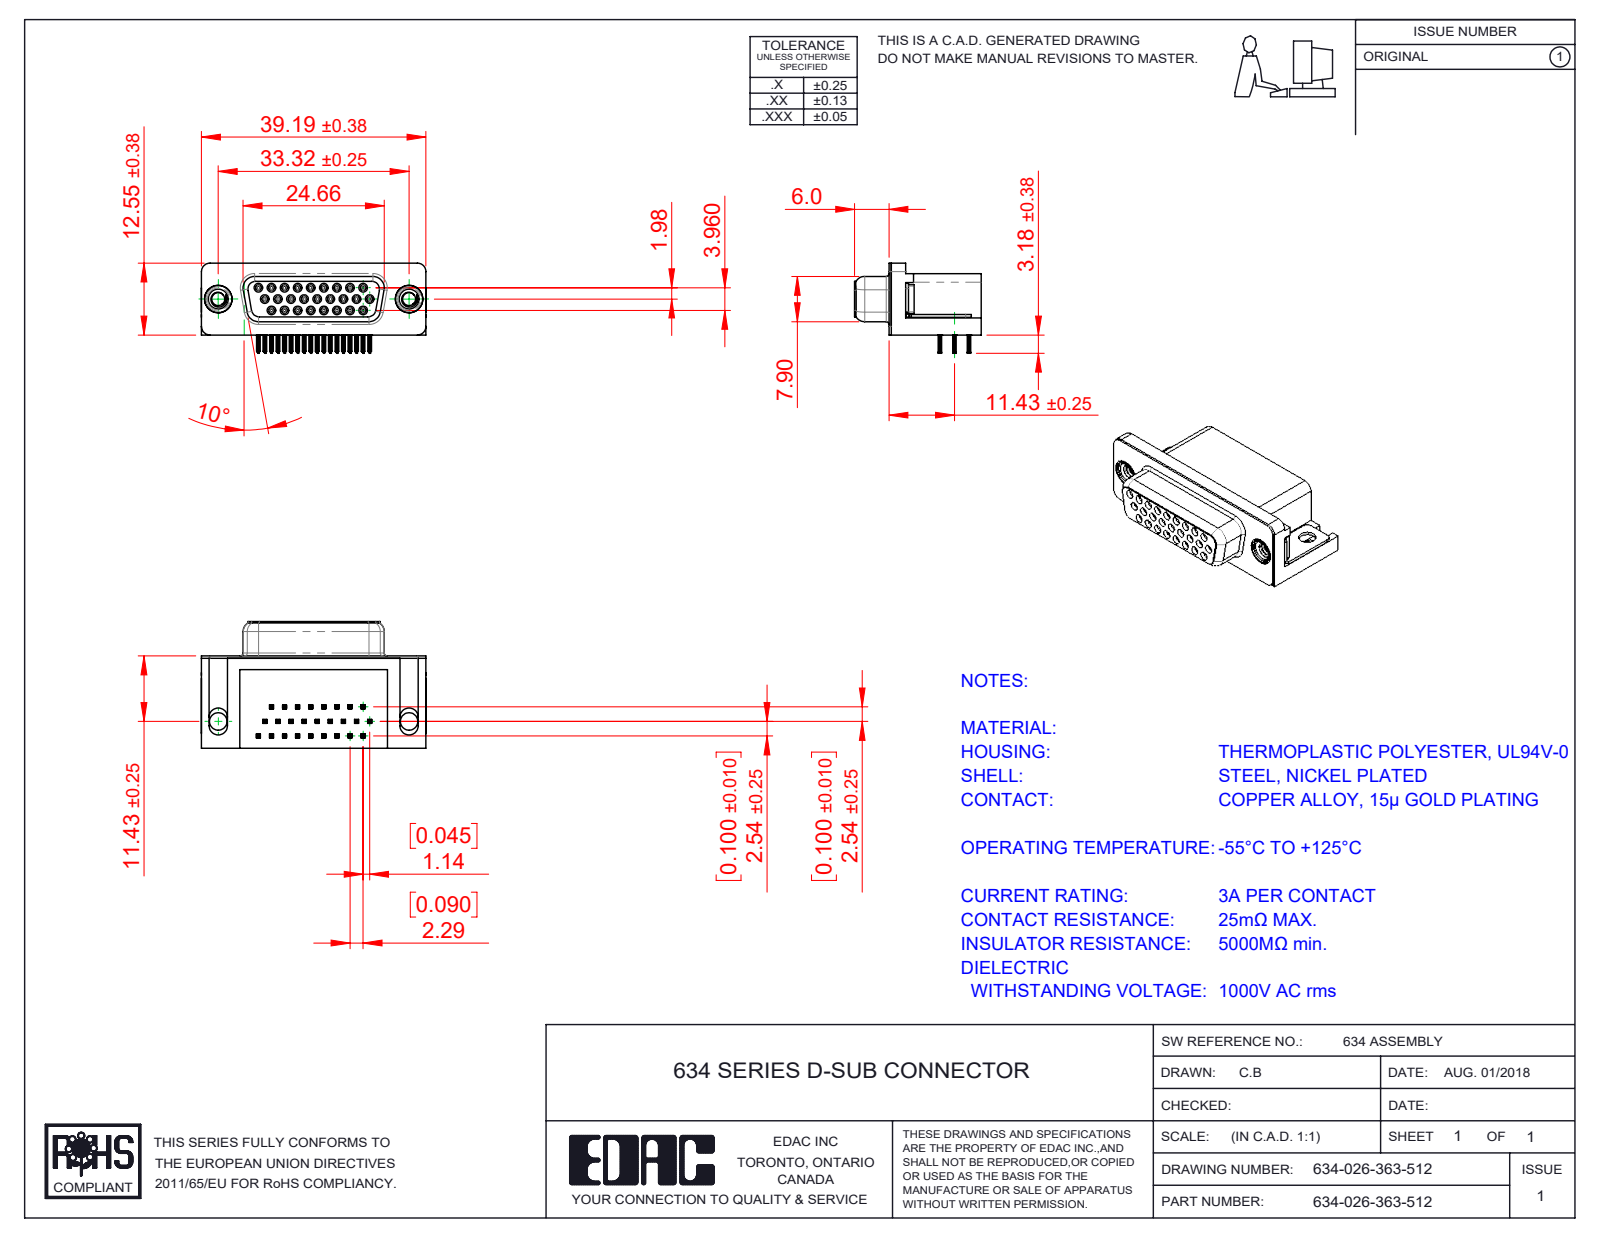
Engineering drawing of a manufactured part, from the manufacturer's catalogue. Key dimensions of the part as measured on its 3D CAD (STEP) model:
Part name (STEP PRODUCT): 634 Housing_26 Socket; Contact Middle; 634-026-363-512; Thru Hole Board Mount (+4 more)
STEP written by: SolidWorks 2016 (CONFIG_CONTROL_DESIGN)
Units: millimetres
Bodies: 32 solids, 3979 faces (1769 planar, 938 cylindrical, 1272 other)
Overall size (bounding box): 39.22 × 22.1 × 15.73
Volume: 6 365 mm³ · Surface area: 9 068 mm²
Round holes (diameter × count): ⌀0.8 ×26, ⌀0.9 ×26, ⌀2.26 ×2, ⌀3.05 ×2, ⌀4 ×2, ⌀4.8 ×2, ⌀5 ×2
Round bosses / shafts (diameter × count): ⌀1.2 ×26, ⌀4.9 ×2, ⌀4.75 ×2, ⌀3.9 ×2
Partial cylindrical surfaces — rounded edges, fillets, slot ends (radius × count): R0.1 ×208, R0.15 ×104, R0.35 ×52, R0.34 ×26, R1 ×19, R0.25 ×8, R0.28 ×8, R1.35 ×8
Main face-to-face distances: 0.4, 10.34, 0.35, 15.7, 16.1, 6.65, 2.5, 0.85, 2.9, 10.69
Hole centre spacings: 2.29, 4.57, 2.28, 3.96, 6.05, 2.3, 2.27, 4.58
